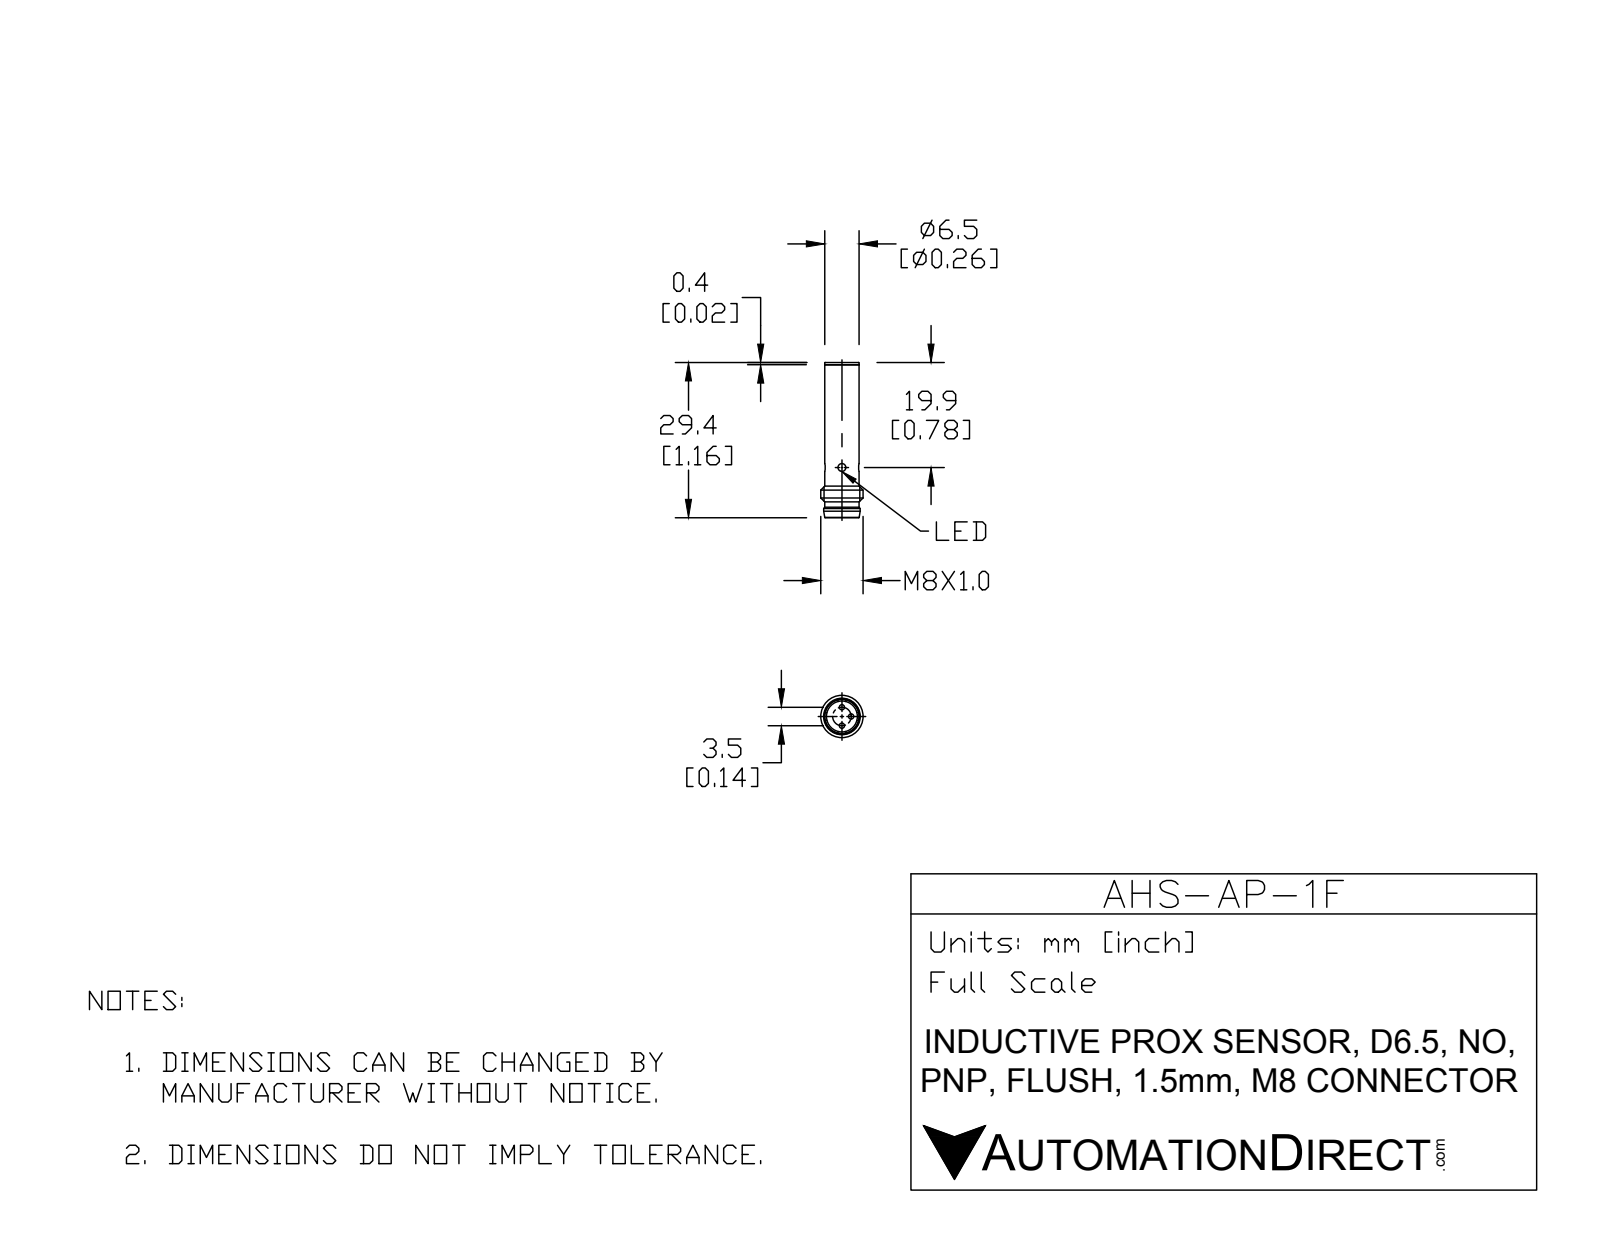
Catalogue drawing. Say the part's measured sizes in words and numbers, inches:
The part is named "AHS-AP-1F". Its 3-D file was written by "SolidWorks 2015 (CONFIG_CONTROL_DESIGN)". It is 4 solids with 56 faces: 12 planar, 26 cylindrical and 18 other. Overall it measures 1.157 by 0.315 by 0.315 inches. Its volume is 0.054 cubic inches and its surface area 1.31 square inches. Round holes: 2 of diameter 0.059, 1 of diameter 0.23. Round bosses or shafts: 3 of diameter 0.039, 1 of diameter 0.315, 1 of diameter 0.272, 1 of diameter 0.256. The main face-to-face distances are 0.961, 0.118, 1.079, 0.217, 0.079, 0.197, 1.157, 1.142, 1.063, 0.945.
